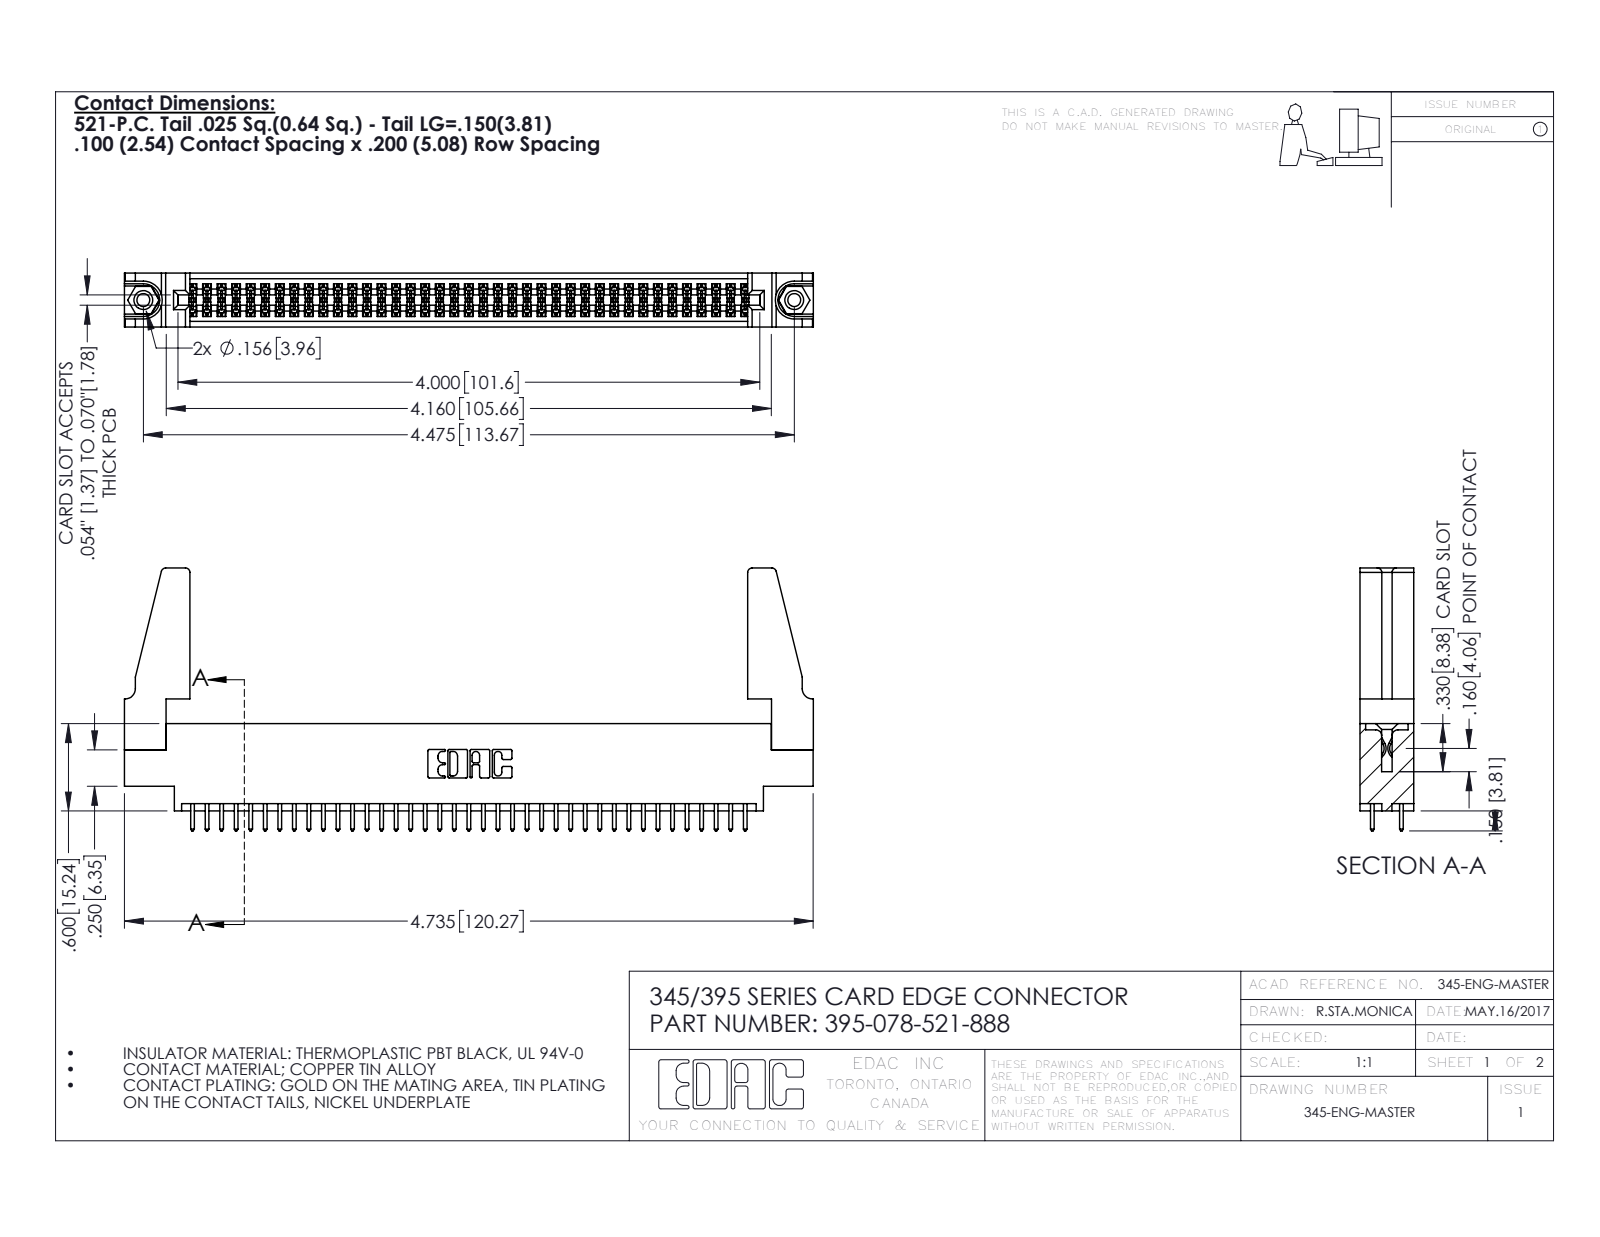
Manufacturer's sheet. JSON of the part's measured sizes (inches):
{"part_name": "345-250-001_345-250-001-102; 345 Part_0.170 Offset - 0.156 Dia-TH; 395-078-521-888; 345-220-078_345-220-088 (+1 more)", "step_written_by": "SolidWorks 2016 (CONFIG_CONTROL_DESIGN)", "units": "inches", "bodies": {"solids": 83, "faces": 4154, "planar": 2730, "cylindrical": 1408, "other": 16}, "overall_size": [4.736, 1.807, 0.37], "volume_in3": 0.901, "surface_area_in2": 31.03, "round_holes": [[0.089, 2], [0.125, 2], [0.156, 2], [0.064, 1]], "round_bosses_or_shafts": [[0.155, 2]], "partial_cylinders_radius": [[0.006, 117], [0.01, 78], [0.01, 22], [0.03, 8], [0.007, 6], [0.031, 6], [0.026, 3], [0.014, 2]], "face_to_face_distances": [0.072, 0.298, 0.37, 0.2, 0.098, 0.272, 0.025, 0.225, 0.175, 0.149], "hole_center_spacings": [0.27, 4.239, 4.475]}
